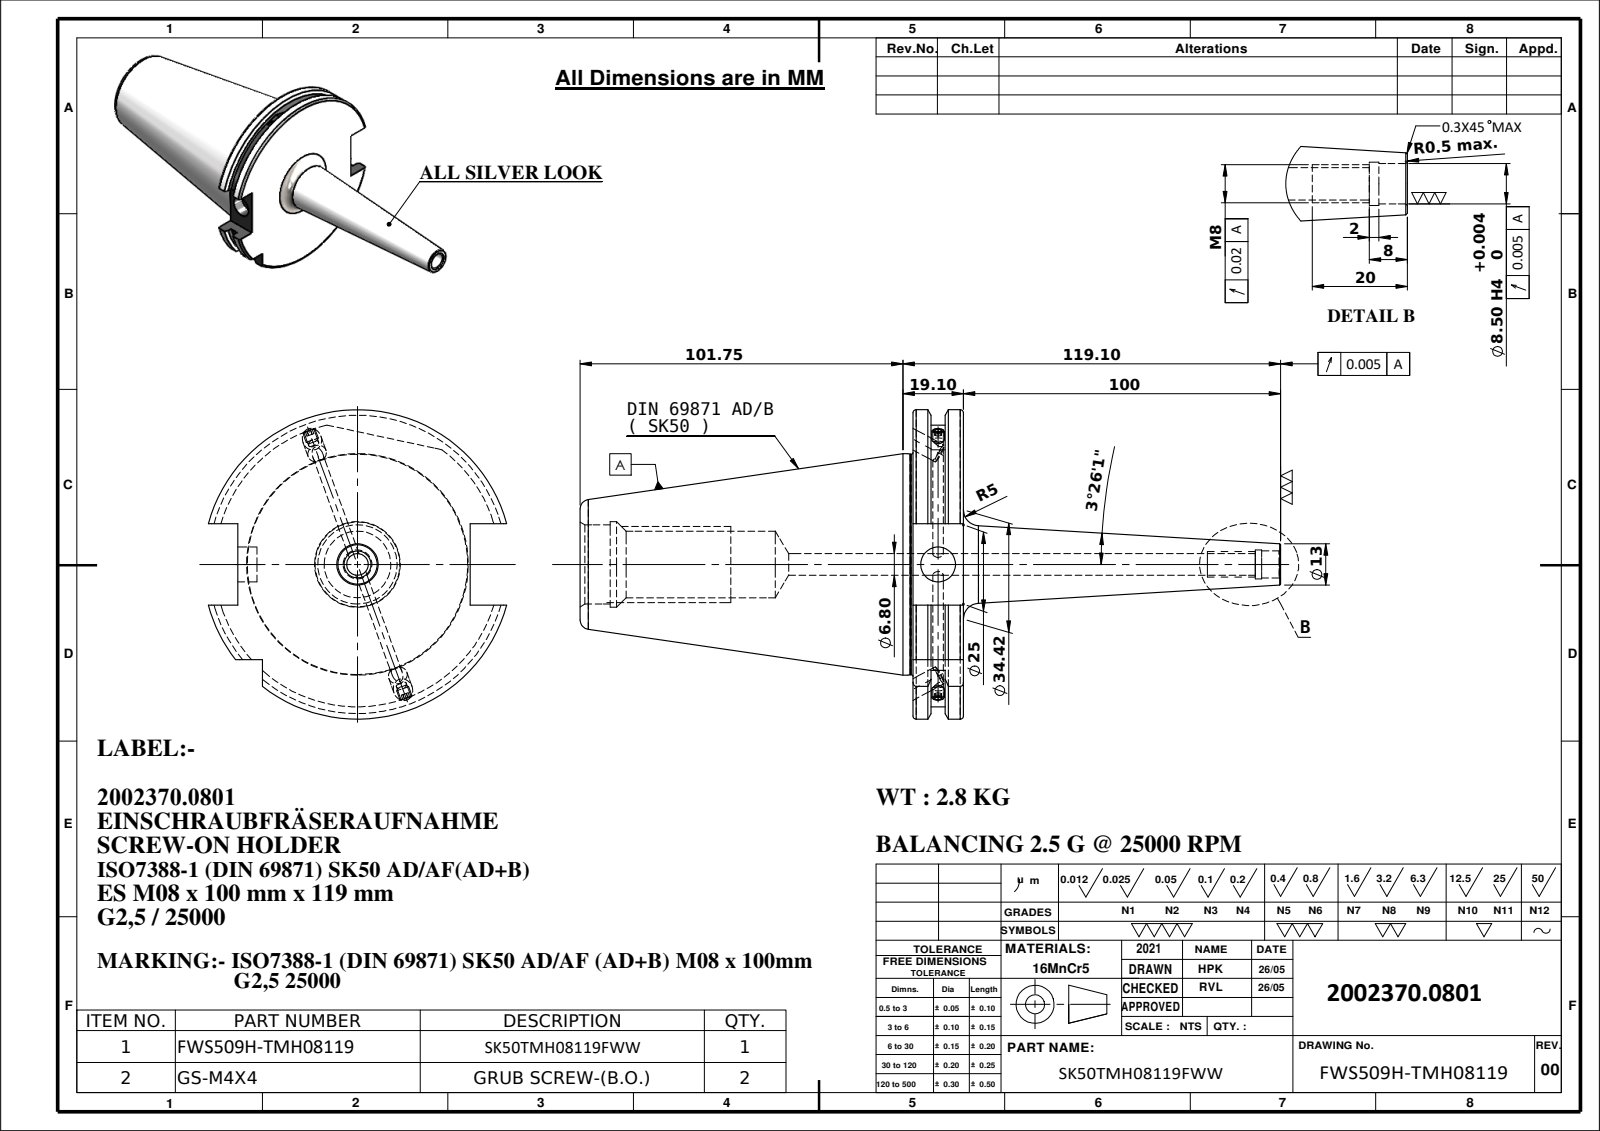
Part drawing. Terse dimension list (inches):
name: SK50TMH08119FWW; M4X4_DIN 913 - M4 x 4-N; 91506-ES7M08100
written by: SolidWorks 2018 (CONFIG_CONTROL_DESIGN)
unit: in
bodies: 3 solids, 138 faces (43 planar, 47 cylindrical, 48 other)
size: 8.695 × 3.839 × 3.703
volume: 22.05 in³; area: 78.64 in²
holes: 2× ⌀0.236, 1× ⌀0.13, 1× ⌀0.268, 1× ⌀0.335, 1× ⌀0.358, 1× ⌀0.433, 1× ⌀0.827, 1× ⌀0.984, 1× ⌀1.063
bosses: 2× ⌀0.157, 1× ⌀2.75, 1× ⌀2.734
rounds: 1× R1.768, 1× R1.919
face distances: 0.626, 0.222, 0.404, 0.399, 0.177, 0.227, 4.132, 4.354, 4.531, 4.758
